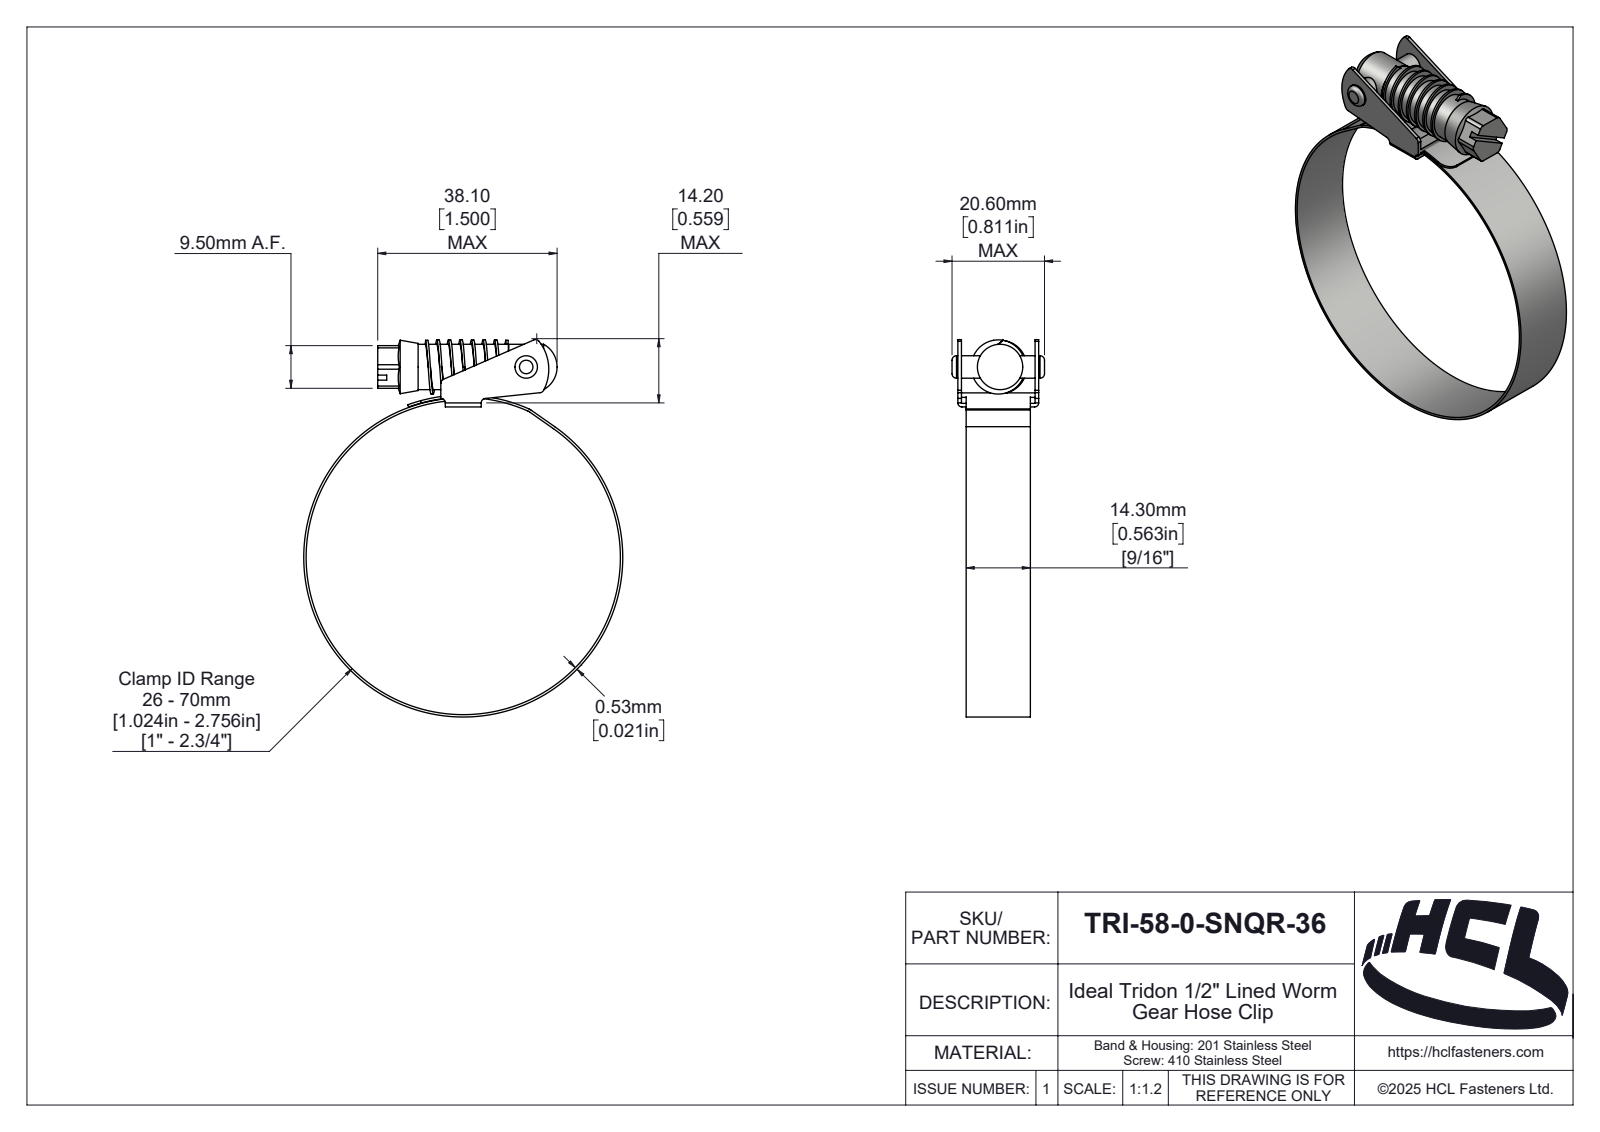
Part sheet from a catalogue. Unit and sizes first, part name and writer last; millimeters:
Units: millimetres
Overall size (bounding box): 84.02 × 71.06 × 20.6
Round holes (diameter × count): ⌀5 ×1, ⌀70 ×1
Round bosses / shafts (diameter × count): ⌀71.06 ×1, ⌀10.1 ×1
Partial cylindrical surfaces — rounded edges, fillets, slot ends (radius × count): R1 ×11, R0.1 ×2, R0.9 ×2, R3 ×2, R0.46 ×1, R1.89 ×1, R2 ×1, R2.35 ×1
Main face-to-face distances: 0.8, 17.2, 1.85, 16.15, 1.05, 15.35, 18, 16.4, 1, 14.3
Hole centre spacings: 44.66
Volume: 5 597 mm³ · Surface area: 10 901 mm²
Bodies: 5 solids, 222 faces (44 planar, 112 cylindrical, 66 other)
Part name (STEP PRODUCT): TRI-58-0-SNQR-36
STEP written by: SolidWorks 2025 (AUTOMOTIVE_DESIGN)
